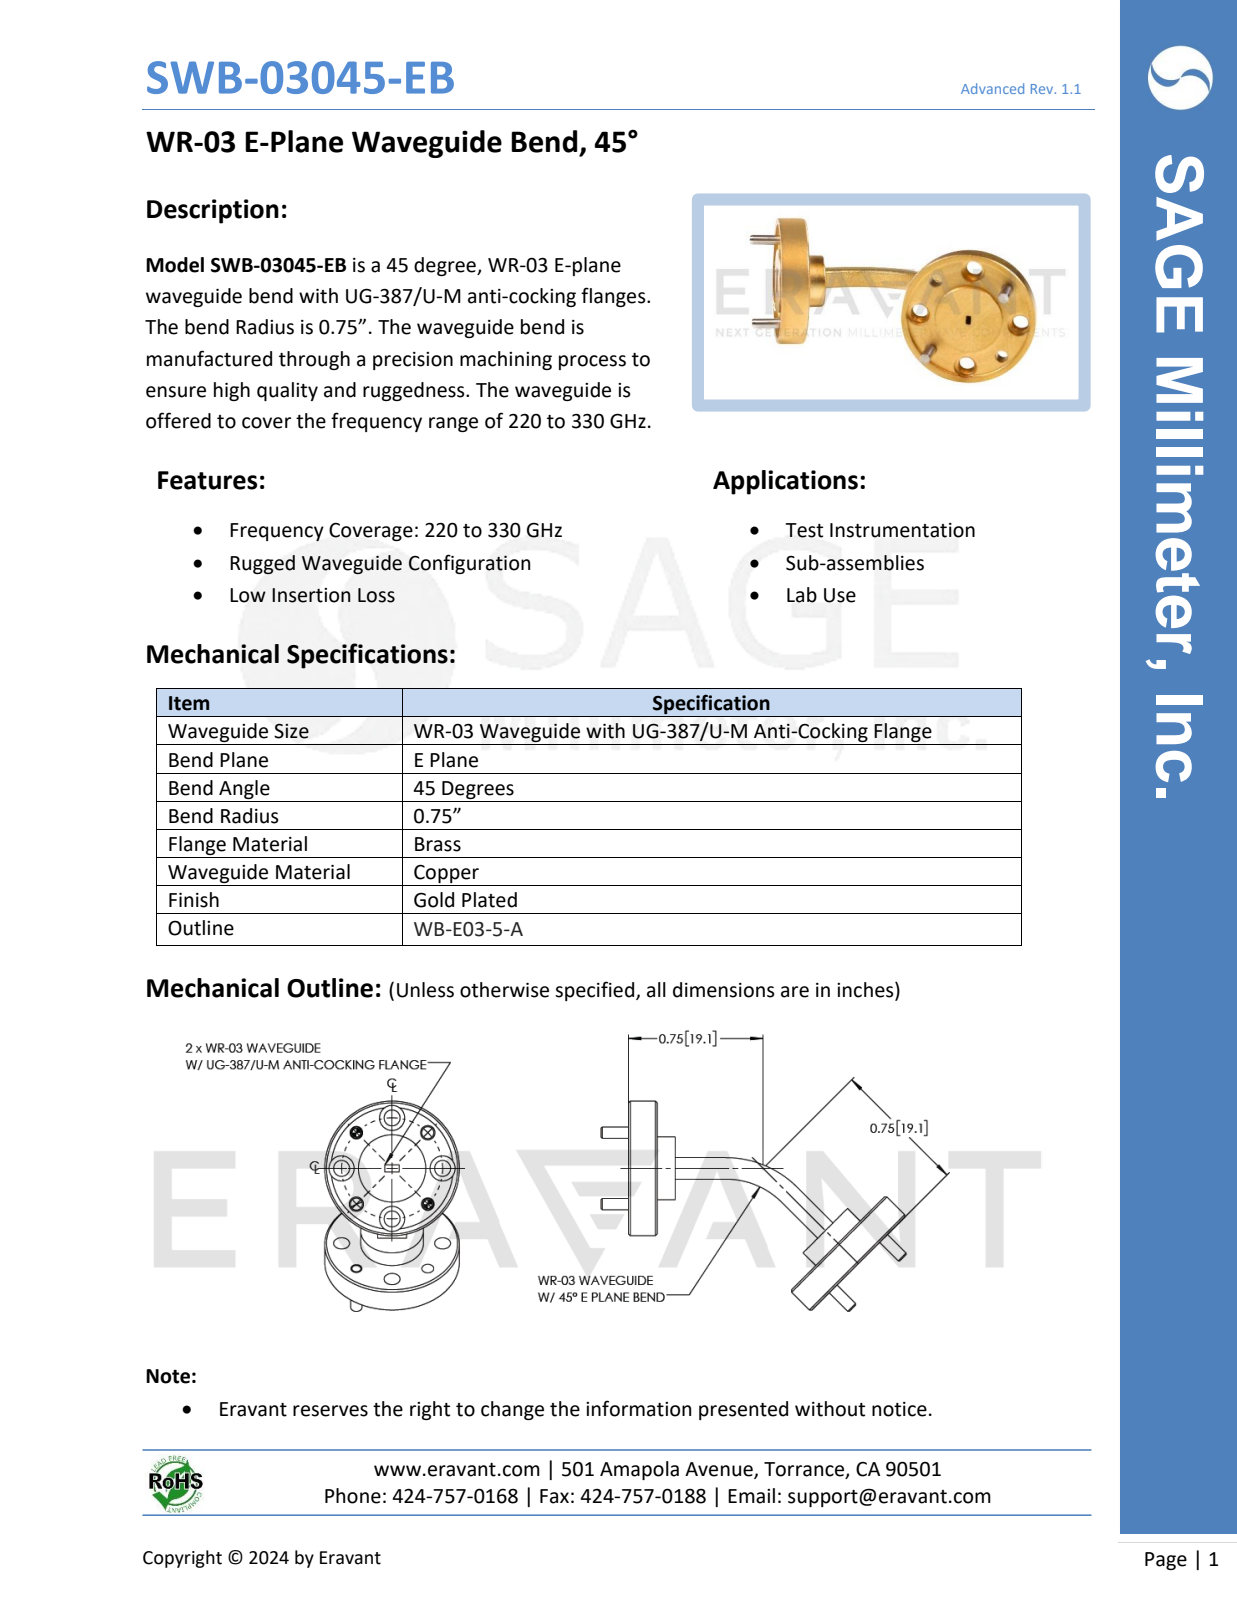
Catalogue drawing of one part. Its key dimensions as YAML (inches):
part_name: "WB-E03-5, defeatured_02"
step_written_by: "SolidWorks 2021 (AUTOMOTIVE_DESIGN)"
units: inches
bodies: {solids: 5, faces: 158, planar: 38, cylindrical: 80, other: 40}
overall_size: [1.699, 1.171, 0.75]
volume: 0.148
surface_area: 4.057
round_holes:
  - {diameter: 0.089, count: 8}
  - {diameter: 0.14, count: 8}
  - {diameter: 0.061, count: 4}
  - {diameter: 0.067, count: 4}
  - {diameter: 0.68, count: 2}
round_bosses_or_shafts:
  - {diameter: 0.063, count: 4}
  - {diameter: 0.75, count: 2}
  - {diameter: 0.35, count: 2}
  - {diameter: 0.375, count: 1}
  - {diameter: 0.375, count: 1}
partial_cylinders:
  - {radius: 0.451, count: 1}
  - {radius: 0.491, count: 1}
  - {radius: 0.509, count: 1}
  - {radius: 0.549, count: 1}
face_to_face_distances: [0.16, 0.1, 0.14, 0.13, 0.26, 0.03, 0.02, 0.04, 0.114, 0.24]
hole_center_spacings: [0.215, 0.281, 0.398, 0.52, 0.519, 0.562, 0.281, 0.398]
